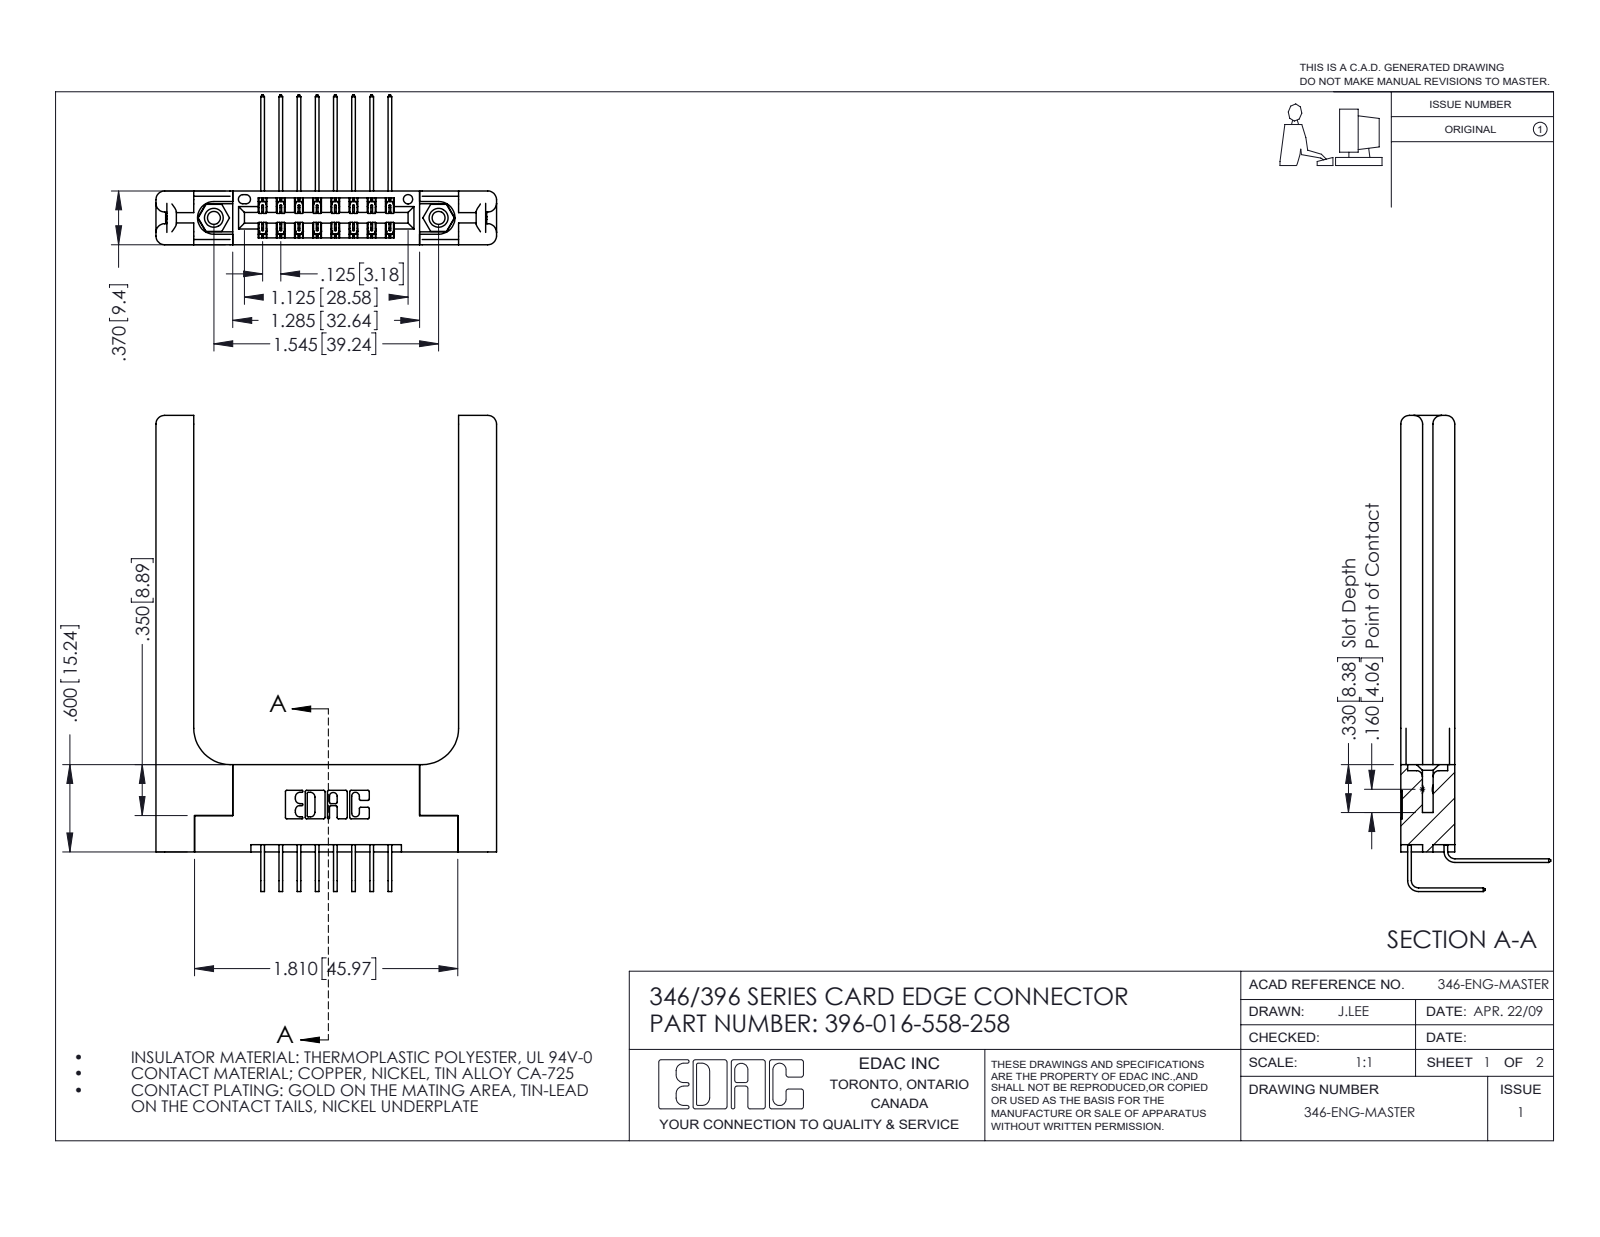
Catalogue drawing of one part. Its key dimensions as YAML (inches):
part_name: "346 Part_Flush Mounting Lugs - 0.156 Dia-TH; 345-292-001_558 559 Tail - 1; 346-220-058_345-220-058; 396-016-558-258 (+2 more)"
step_written_by: "SolidWorks 2016 (CONFIG_CONTROL_DESIGN)"
units: inches
bodies: {solids: 21, faces: 1242, planar: 816, cylindrical: 366, other: 60}
overall_size: [3.273, 2.341, 1.03]
volume: 0.801
surface_area: 19.55
round_holes:
  - {diameter: 0.089, count: 2}
  - {diameter: 0.125, count: 2}
  - {diameter: 0.156, count: 2}
  - {diameter: 0.064, count: 1}
round_bosses_or_shafts:
  - {diameter: 0.155, count: 2}
partial_cylinders:
  - {radius: 0.006, count: 24}
  - {radius: 0.01, count: 22}
  - {radius: 0.06, count: 16}
  - {radius: 0.007, count: 6}
  - {radius: 0.031, count: 6}
  - {radius: 0.026, count: 3}
  - {radius: 0.014, count: 2}
  - {radius: 0.022, count: 2}
face_to_face_distances: [0.37, 0.15, 0.072, 0.22, 0.322, 0.148, 0.048, 0.25, 0.102, 0.173]
hole_center_spacings: [0.246, 1.341, 1.545]
